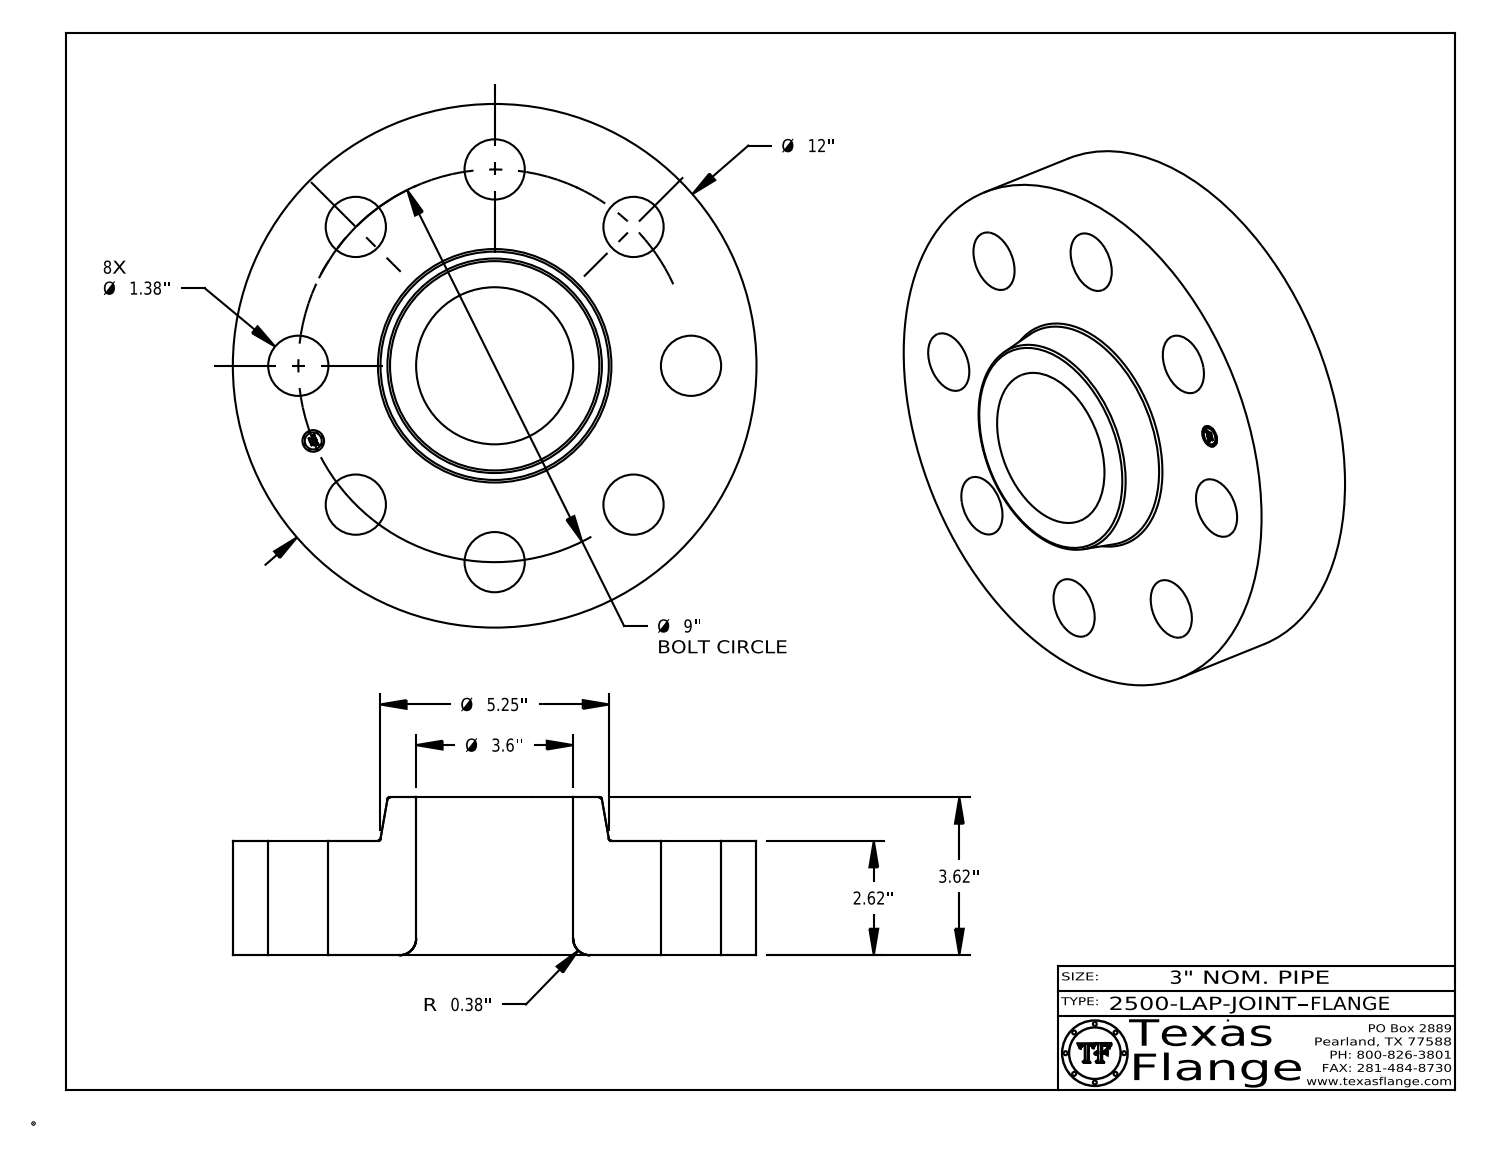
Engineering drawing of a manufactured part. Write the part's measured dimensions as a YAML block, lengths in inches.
part_name: "2500-LAP-JOINT FLANGE"
step_written_by: "CATIA V5 STEP AP214 (AUTOMOTIVE_DESIGN)"
units: inches
bodies: {solids: 1, faces: 416, planar: 368, cylindrical: 40, other: 8}
overall_size: [12, 12, 3.62]
volume: 248
surface_area: 423.6
round_holes:
  - {diameter: 1.38, count: 8}
  - {diameter: 0.495, count: 1}
  - {diameter: 3.6, count: 1}
round_bosses_or_shafts:
  - {diameter: 0.03, count: 8}
  - {diameter: 12, count: 1}
  - {diameter: 0.39, count: 1}
face_to_face_distances: [2.62, 3.62, 1, 2.605, 0.015, 1.015, 0.148, 0.144, 0.027, 0.096]
hole_center_spacings: [4.5, 3.444, 6.364, 8.315, 1.756, 5, 7.483, 9]
